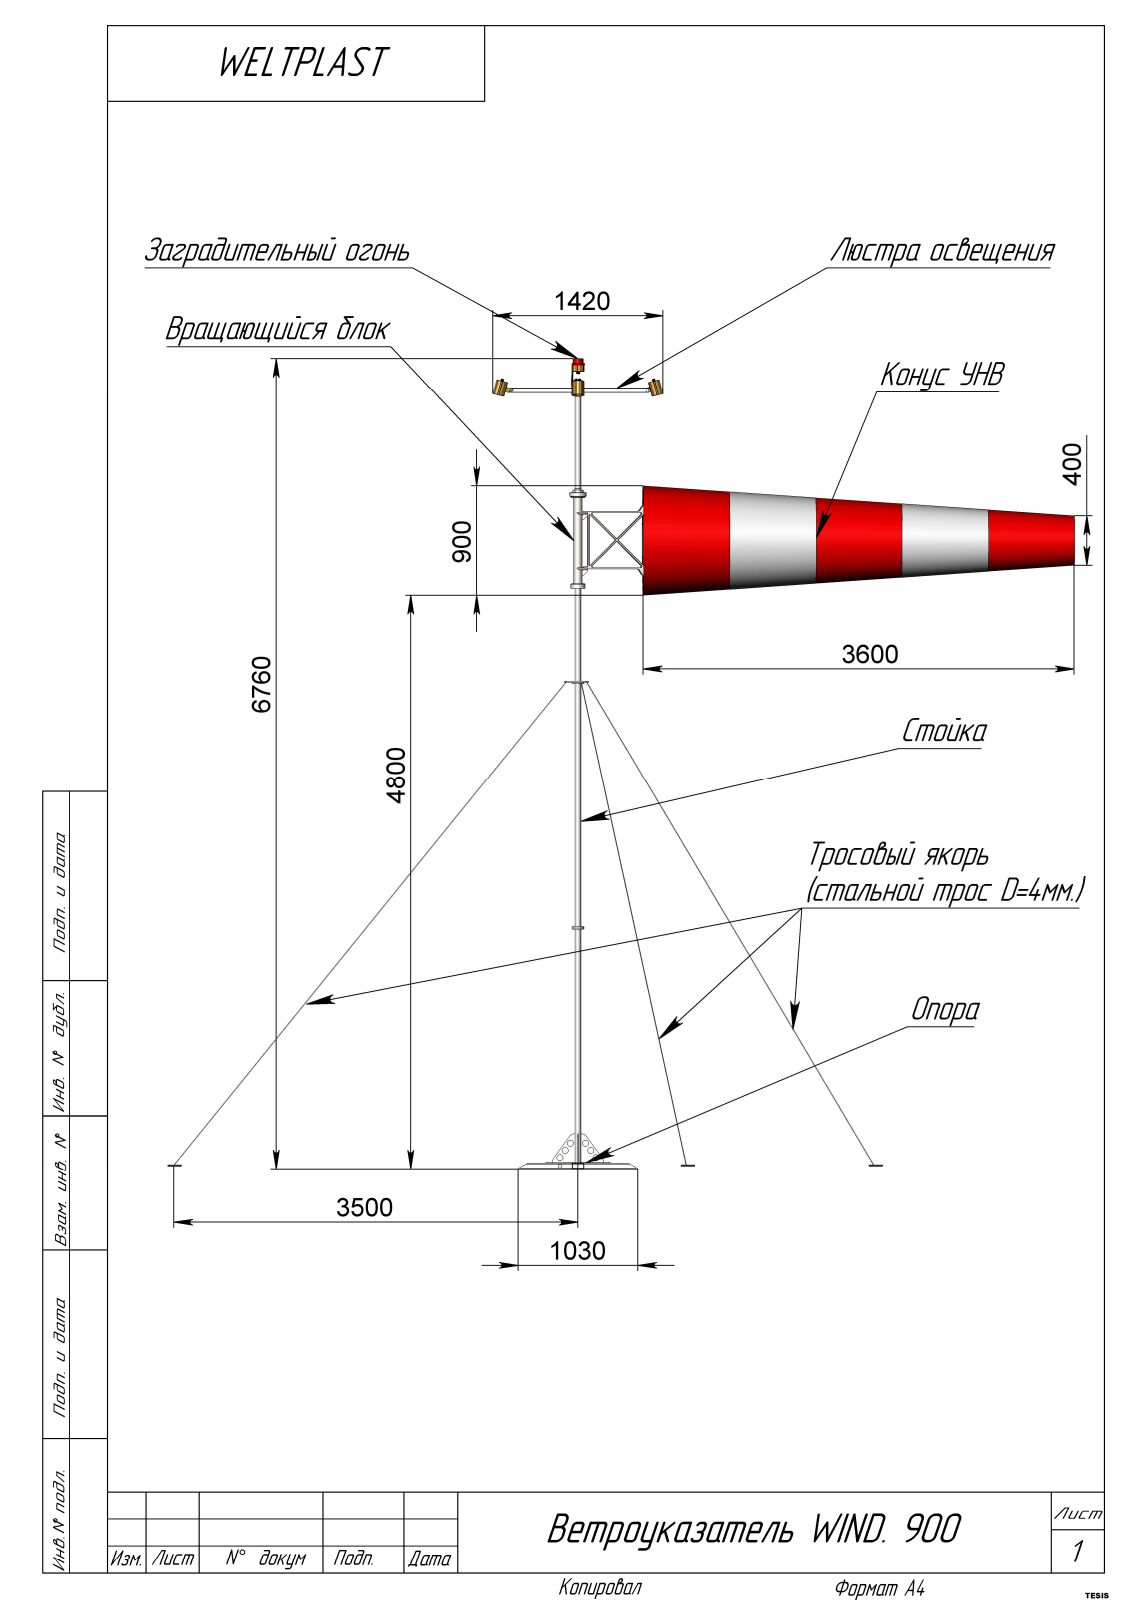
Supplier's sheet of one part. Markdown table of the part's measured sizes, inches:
| quantity | value |
| --- | --- |
| part name | Корпус_11; WIND.008 Труба остова; подшипник 1212 сферический макет.; WIND.022 (Кронштейн-пластина фонаря) (+8 more) |
| STEP written by | SolidWorks 2017 (AUTOMOTIVE_DESIGN) |
| units | inches |
| bodies | 93 solids, 2451 faces (722 planar, 1569 cylindrical, 160 other) |
| overall size | 298.531 × 266.102 × 235.33 |
| volume | 155 000 in³ |
| surface area | 83 060 in² |
| round holes (diameter × count) | 0.173 × 54, 0.236 × 30, 0.472 × 21, 2.047 × 12, 0.496 × 10, 0.797 × 10, 0.551 × 8, 0.177 × 6, 0.197 × 6, 0.433 × 6, 3.11 × 5, 0.315 × 4 |
| round bosses / shafts (diameter × count) | 0.551 × 12, 0.846 × 10, 0.776 × 10, 0.157 × 3, 5.512 × 1, 4.724 × 1, 3.937 × 1, 3.74 × 1 |
| partial cylindrical surfaces (radius × count) | 0.197 × 139, 0.157 × 64, 0.394 × 26, 0.079 × 20, 0.177 × 18, 0.059 × 14, 0.098 × 12, 0.118 × 10 |
| main face-to-face distances | 0.157, 1.811, 1.654, 141.748, 0.079, 0.394, 2.205, 1.496, 0.236, 0.433 |
| hole center spacings | 1.87, 3.239, 1.319, 2.421, 3.74, 1.102, 1.664, 2.198 |
